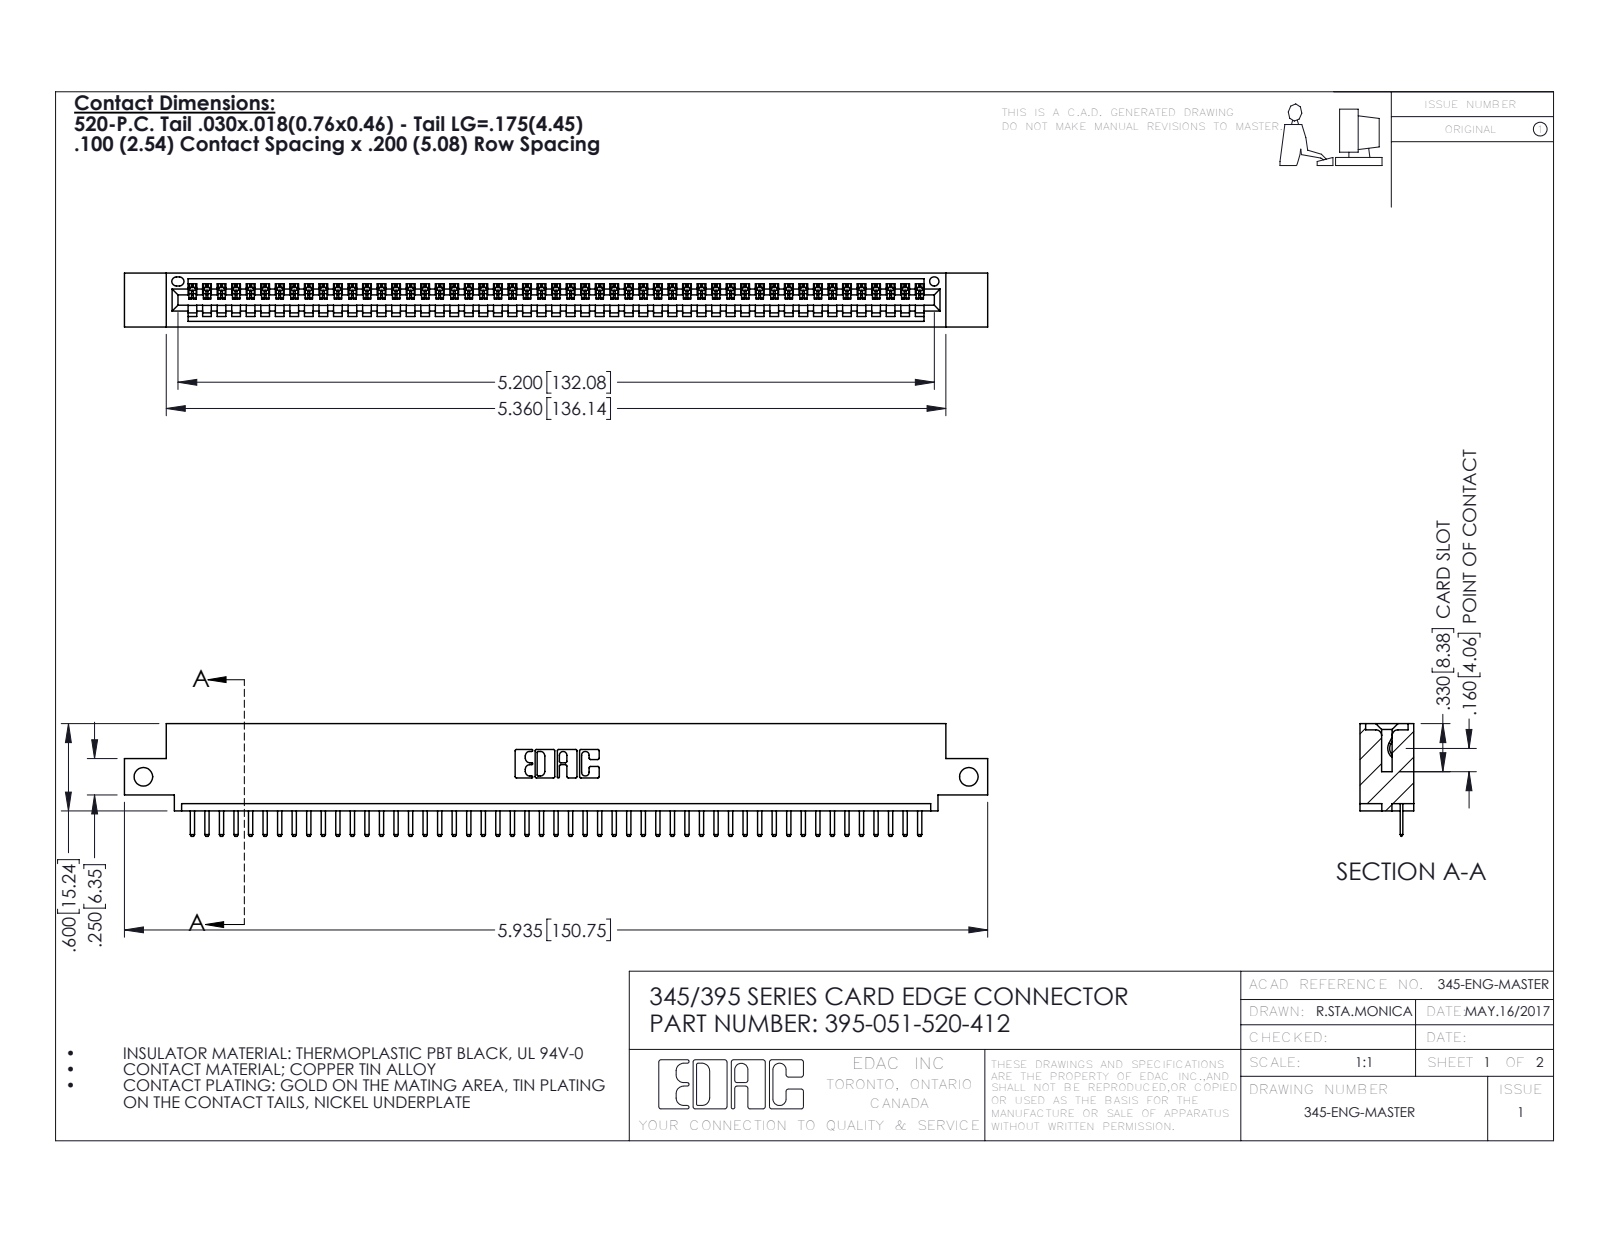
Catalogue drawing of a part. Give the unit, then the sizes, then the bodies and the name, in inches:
Units: inches
Overall size (bounding box): 5.935 × 0.775 × 0.37
Round holes (diameter × count): ⌀0.128 ×2, ⌀0.064 ×1
Partial cylindrical surfaces — rounded edges, fillets, slot ends (radius × count): R0.01 ×104, R0.006 ×102, R0.01 ×22, R0.007 ×6, R0.031 ×6, R0.026 ×3, R0.031 ×2, R0.04 ×2
Main face-to-face distances: 0.298, 0.072, 0.37, 0.2, 0.098, 0.272, 0.025, 0.225, 0.072, 0.149
Hole centre spacings: 5.675
Volume: 0.859 in³ · Surface area: 28.36 in²
Bodies: 52 solids, 3292 faces (2226 planar, 1066 cylindrical, 0 other)
Part name (STEP PRODUCT): 395-051-520-412; 345-292-001_345-293-120; 345 Part_0.110 Offset - Side Mount
STEP written by: SolidWorks 2016 (CONFIG_CONTROL_DESIGN)
